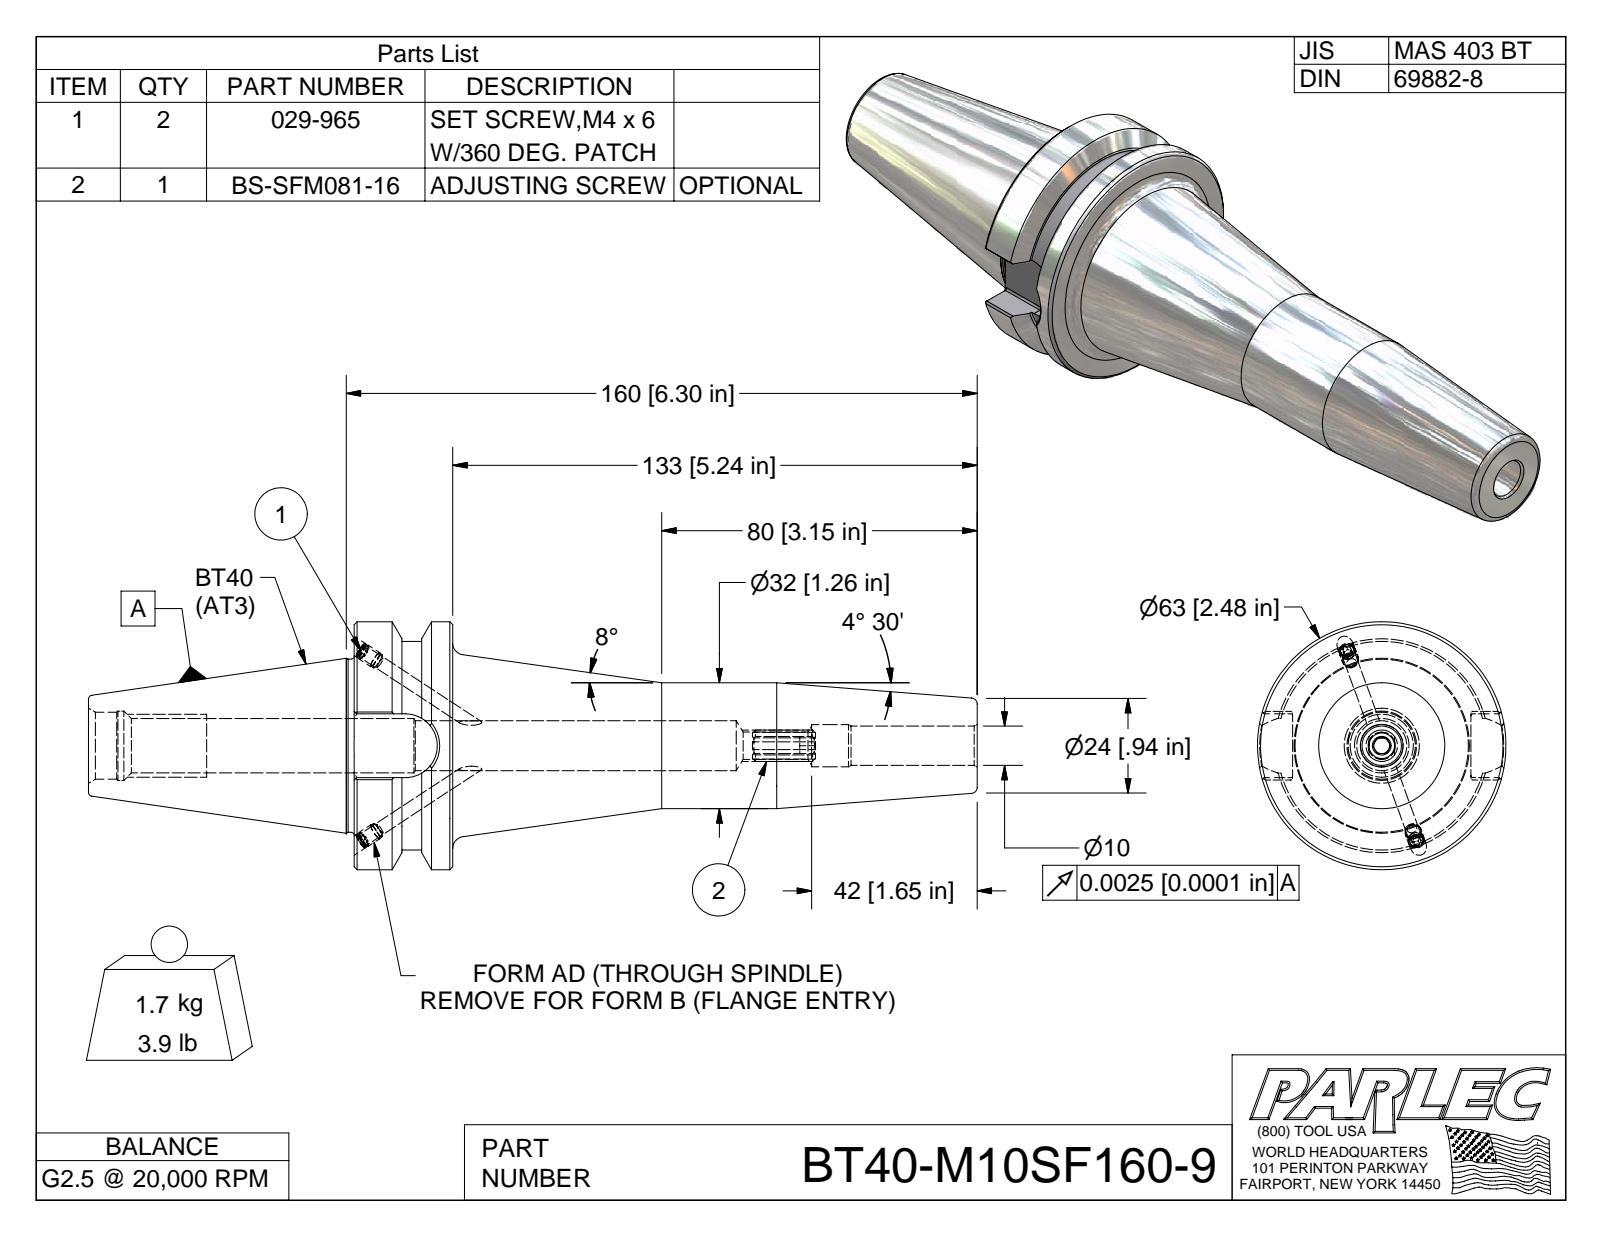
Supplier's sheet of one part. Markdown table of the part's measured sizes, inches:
| quantity | value |
| --- | --- |
| part name | BT40-M10SF160-9; BT40BC-M10SF160-9-1; 029-965; BS-SFM081-16 |
| STEP written by | Autodesk Inventor 2009 (AUTOMOTIVE_DESIGN) |
| units | inches |
| bodies | 4 solids, 134 faces (57 planar, 33 cylindrical, 44 other) |
| overall size | 8.874 × 2.48 × 2.48 |
| volume | 13.85 in³ |
| surface area | 63.91 in² |
| round holes (diameter × count) | 0.13 × 2, 0.161 × 2, 0.393 × 1, 0.423 × 1, 0.694 × 1 |
| round bosses / shafts (diameter × count) | 0.165 × 2, 0.157 × 2, 2.48 × 1, 2.087 × 1, 1.75 × 1, 1.73 × 1, 1.26 × 1 |
| partial cylindrical surfaces (radius × count) | 0.02 × 8, 0.157 × 1, 0.319 × 1 |
| main face-to-face distances | 0.984, 1.78, 6.221, 5.237, 2.653, 3.637, 8.874, 0.637, 0.762, 1.018 |
